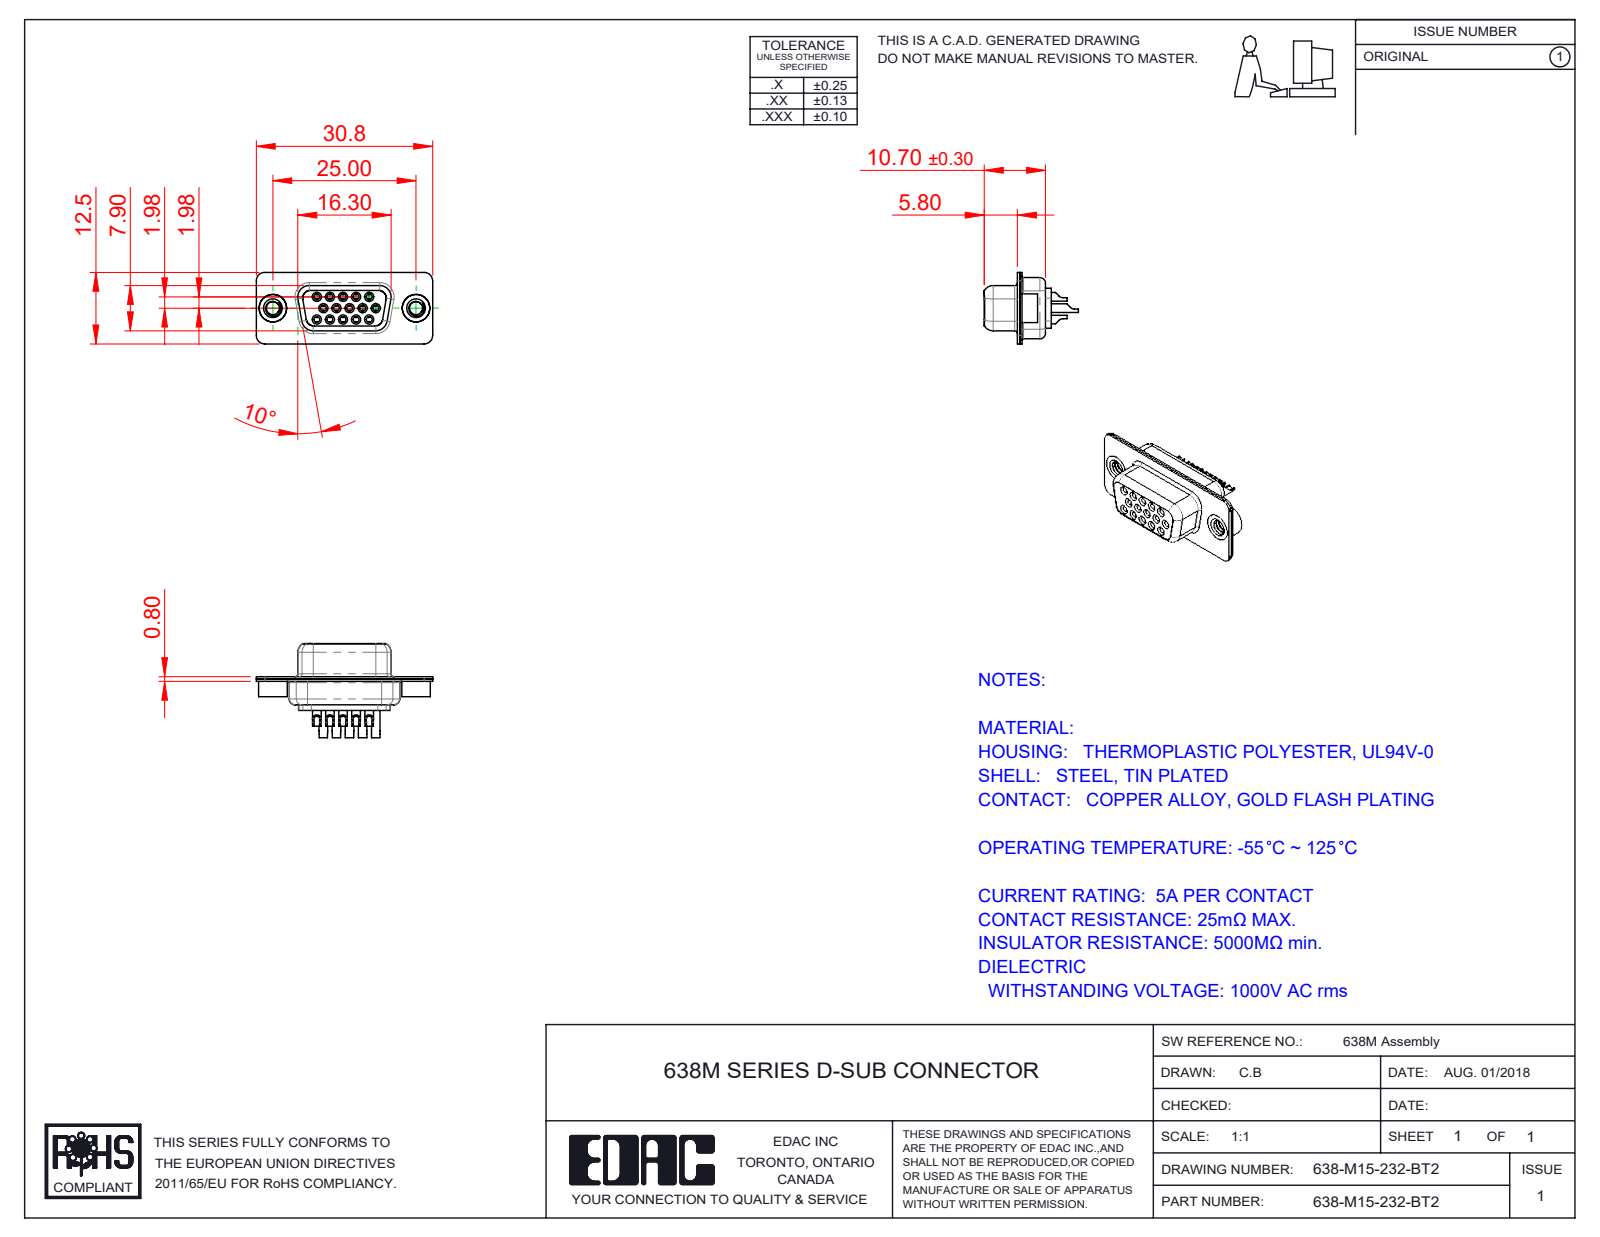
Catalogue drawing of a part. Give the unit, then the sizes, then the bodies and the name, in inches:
Units: inches
Overall size (bounding box): 1.213 × 0.648 × 0.492
Round holes (diameter × count): ⌀0.039 ×16, ⌀0.043 ×15, ⌀0.067 ×15, ⌀0.071 ×15, ⌀0.079 ×15, ⌀0.089 ×2, ⌀0.157 ×2, ⌀0.189 ×2
Round bosses / shafts (diameter × count): ⌀0.087 ×15, ⌀0.063 ×15, ⌀0.059 ×15, ⌀0.197 ×2, ⌀0.193 ×2
Partial cylindrical surfaces — rounded edges, fillets, slot ends (radius × count): R0.059 ×16, R0.079 ×12, R0.053 ×8, R0.063 ×8, R0.039 ×7, R0.01 ×4, R0.02 ×4, R0.024 ×4
Main face-to-face distances: 0.016, 0.055, 0.018, 0.333, 0.039, 0.031, 0.35, 0.071, 0.244, 0.366
Hole centre spacings: 0.09, 0.156, 0.09, 0.18, 0.238, 0.238, 0.27, 0.312
Volume: 0.101 in³ · Surface area: 8.42 in²
Bodies: 20 solids, 1104 faces (322 planar, 452 cylindrical, 330 other)
Part name (STEP PRODUCT): 638M 4-40 Threaded Rivet; 638M Contact Row 3_32; 638M Contact Row 1_32; 638-M15-232-BT2 (+4 more)
STEP written by: SolidWorks 2020 (CONFIG_CONTROL_DESIGN)
